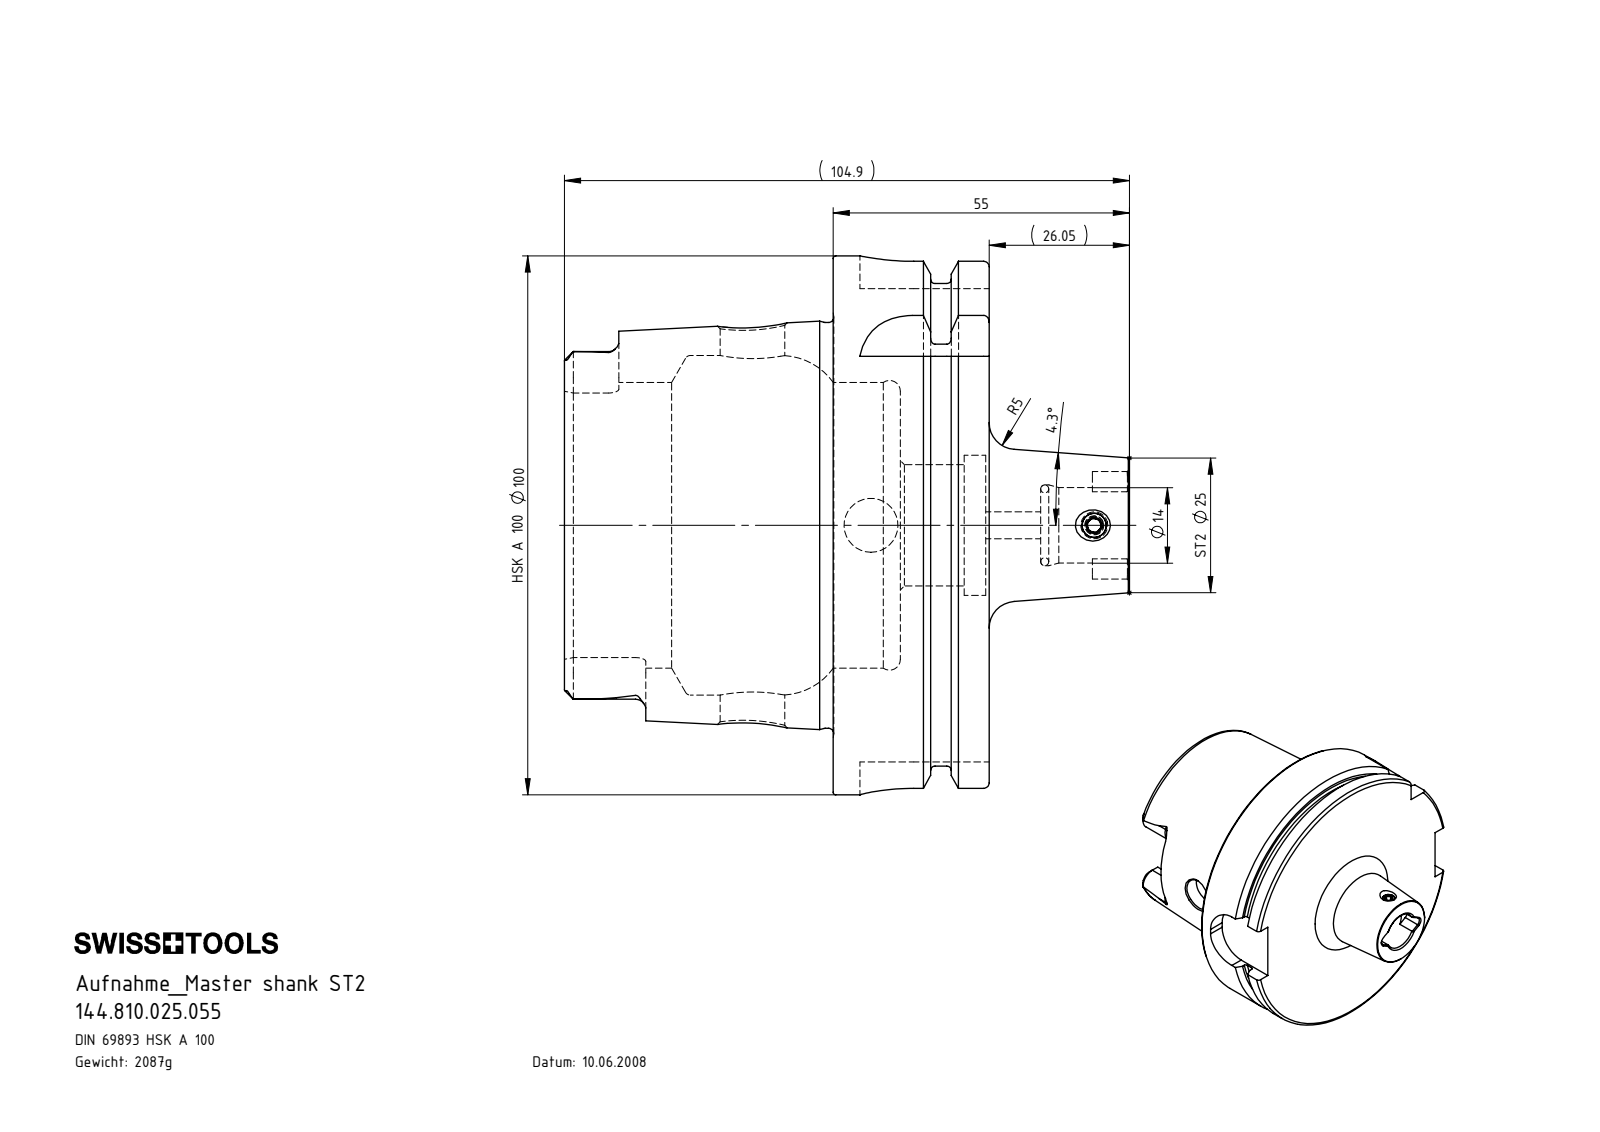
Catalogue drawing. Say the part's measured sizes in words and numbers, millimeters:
The part is named "DIN 3771 - 12x1.5; ST2-ER1.001.006_A; HA0-ST2.K01.055; HA0-ST2.K01.055_A_Fertigbearbeitung". Its 3-D file was written by "SolidWorks 2015 (CONFIG_CONTROL_DESIGN)". It is 3 solids with 202 faces: 57 planar, 57 cylindrical and 88 other. Overall it measures 104.9 by 100 by 100 millimeters. Its volume is 263 853 cubic millimeters and its surface area 52 798 square millimeters. Round holes: 1 of diameter 4.5, 1 of diameter 5, 1 of diameter 10, 1 of diameter 12, 1 of diameter 14, 1 of diameter 15, 1 of diameter 22.5, 1 of diameter 26, 1 of diameter 53, 1 of diameter 63. Round bosses or shafts: 1 of diameter 100, 1 of diameter 91.95, 1 of diameter 75.26, 1 of diameter 25, 1 of diameter 5. Partial cylindrical surfaces (rounded edges, fillets, slot ends): 6 of radius 1.9, 4 of radius 4.88, 4 of radius 10, 2 of radius 1.8. The main face-to-face distances are 28.95, 16.5, 12.45, 49.9, 62.35, 78.85, 78.2, 28.3, 15.85, 0.65. The hole center spacings are 41.45.
